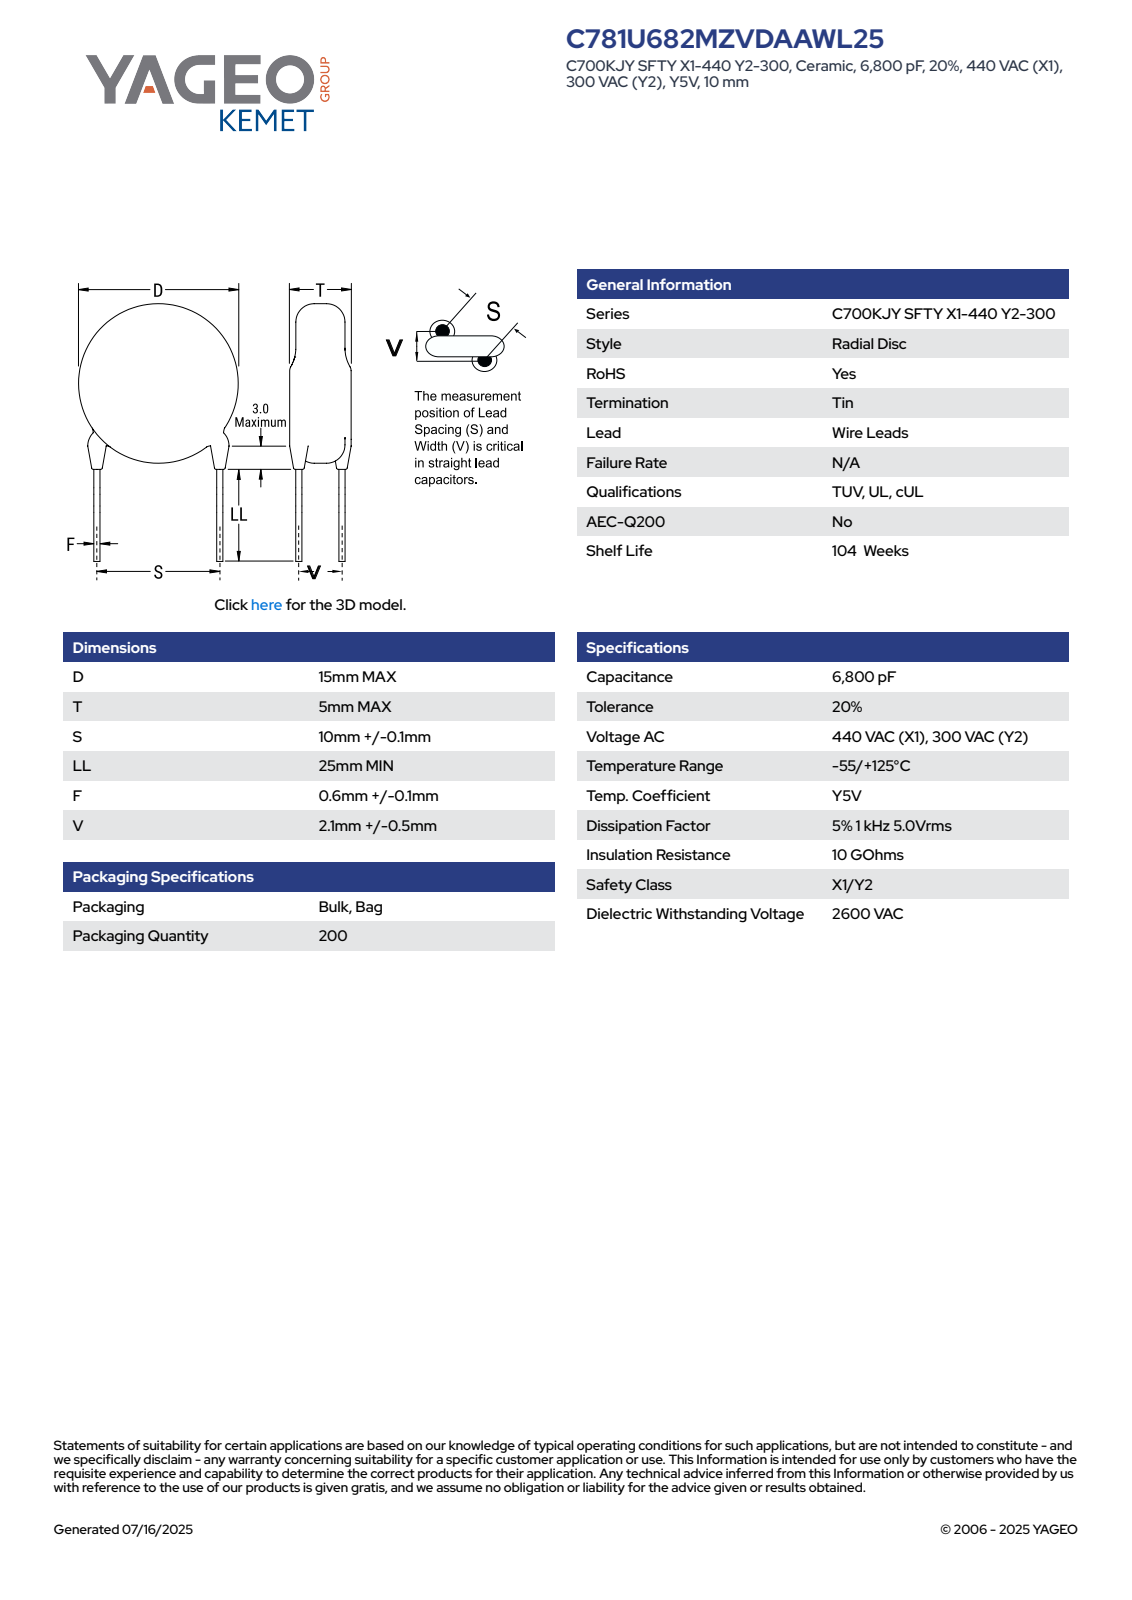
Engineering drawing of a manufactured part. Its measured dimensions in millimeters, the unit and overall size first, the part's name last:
Units: millimetres
Overall size (bounding box): 40.19 × 15 × 5
Round bosses / shafts (diameter × count): ⌀1.2 ×2, ⌀0.7 ×2, ⌀15 ×1
Main face-to-face distances: 5, 25, 1.75, 33.99, 8.99, 32.24, 7.24, 0.48, 0.43, 0.34
Volume: 888 mm³ · Surface area: 691 mm²
Bodies: 4 solids, 77 faces (63 planar, 10 cylindrical, 4 other)
Part name (STEP PRODUCT): CCD_KST_15X5_D15T5S10.1LL25F0.7V2.1
STEP written by: SolidWorks 2021 (AUTOMOTIVE_DESIGN)
